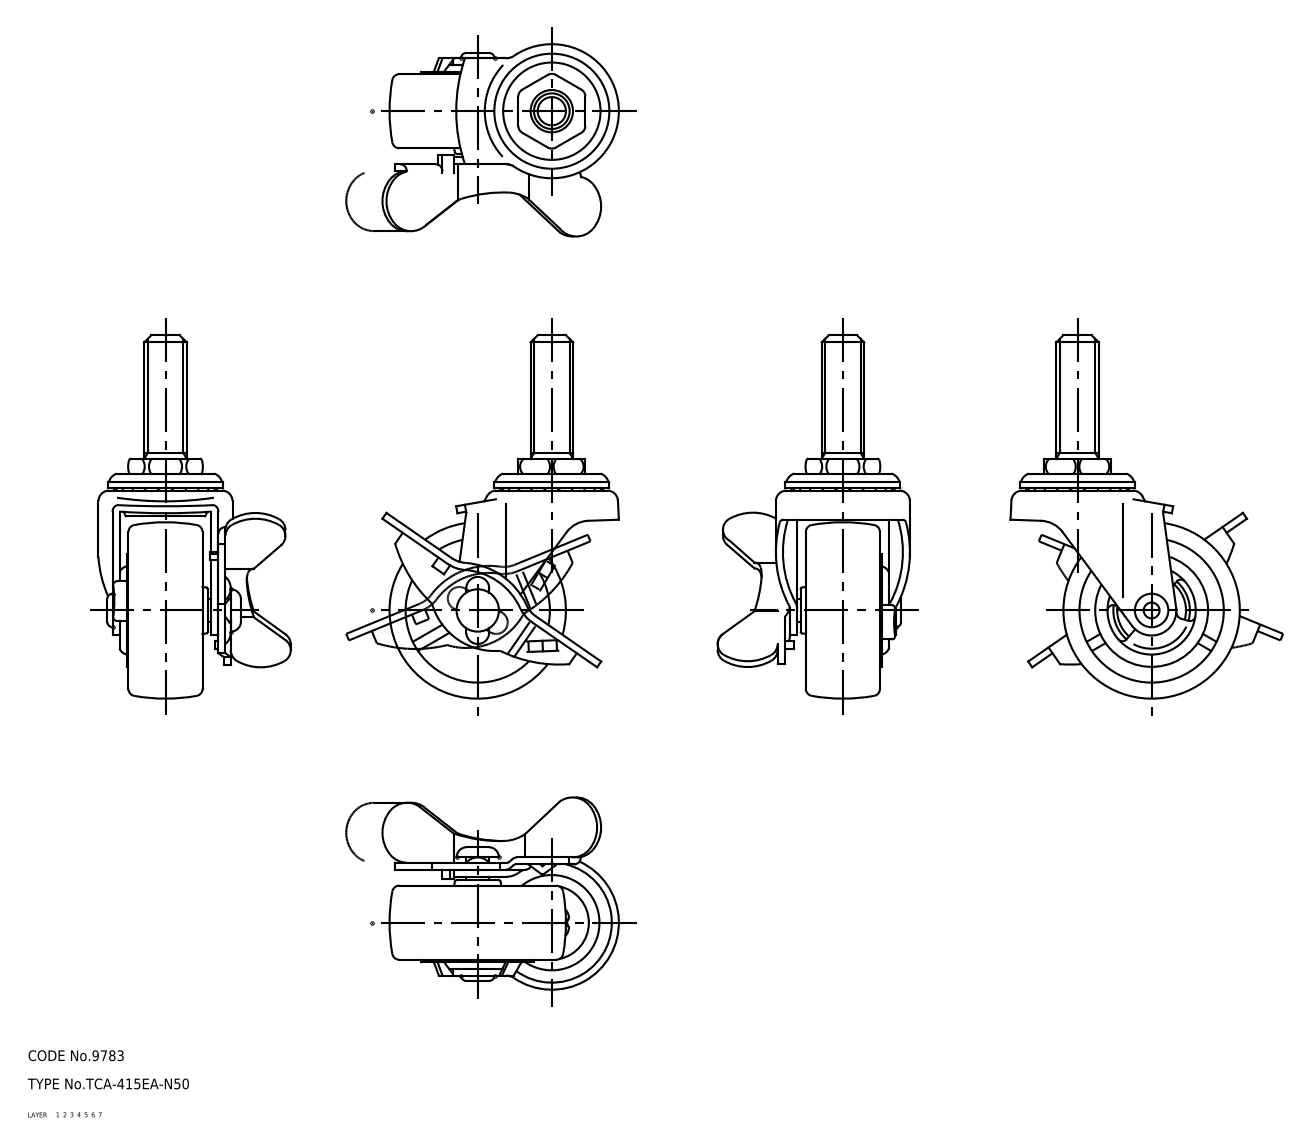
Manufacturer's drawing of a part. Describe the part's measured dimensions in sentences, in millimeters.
The part is named "wheel; mounting plate; main shaft; lever (+2 more)". Its 3-D file was written by "CADfix (AUTOMOTIVE_DESIGN)". It is 6 solids with 459 faces: 0 planar, 0 cylindrical and 459 other. Overall it measures 103 by 67.42 by 54.5 millimeters. Its volume is 52 018 cubic millimeters and its surface area 28 717 square millimeters.
